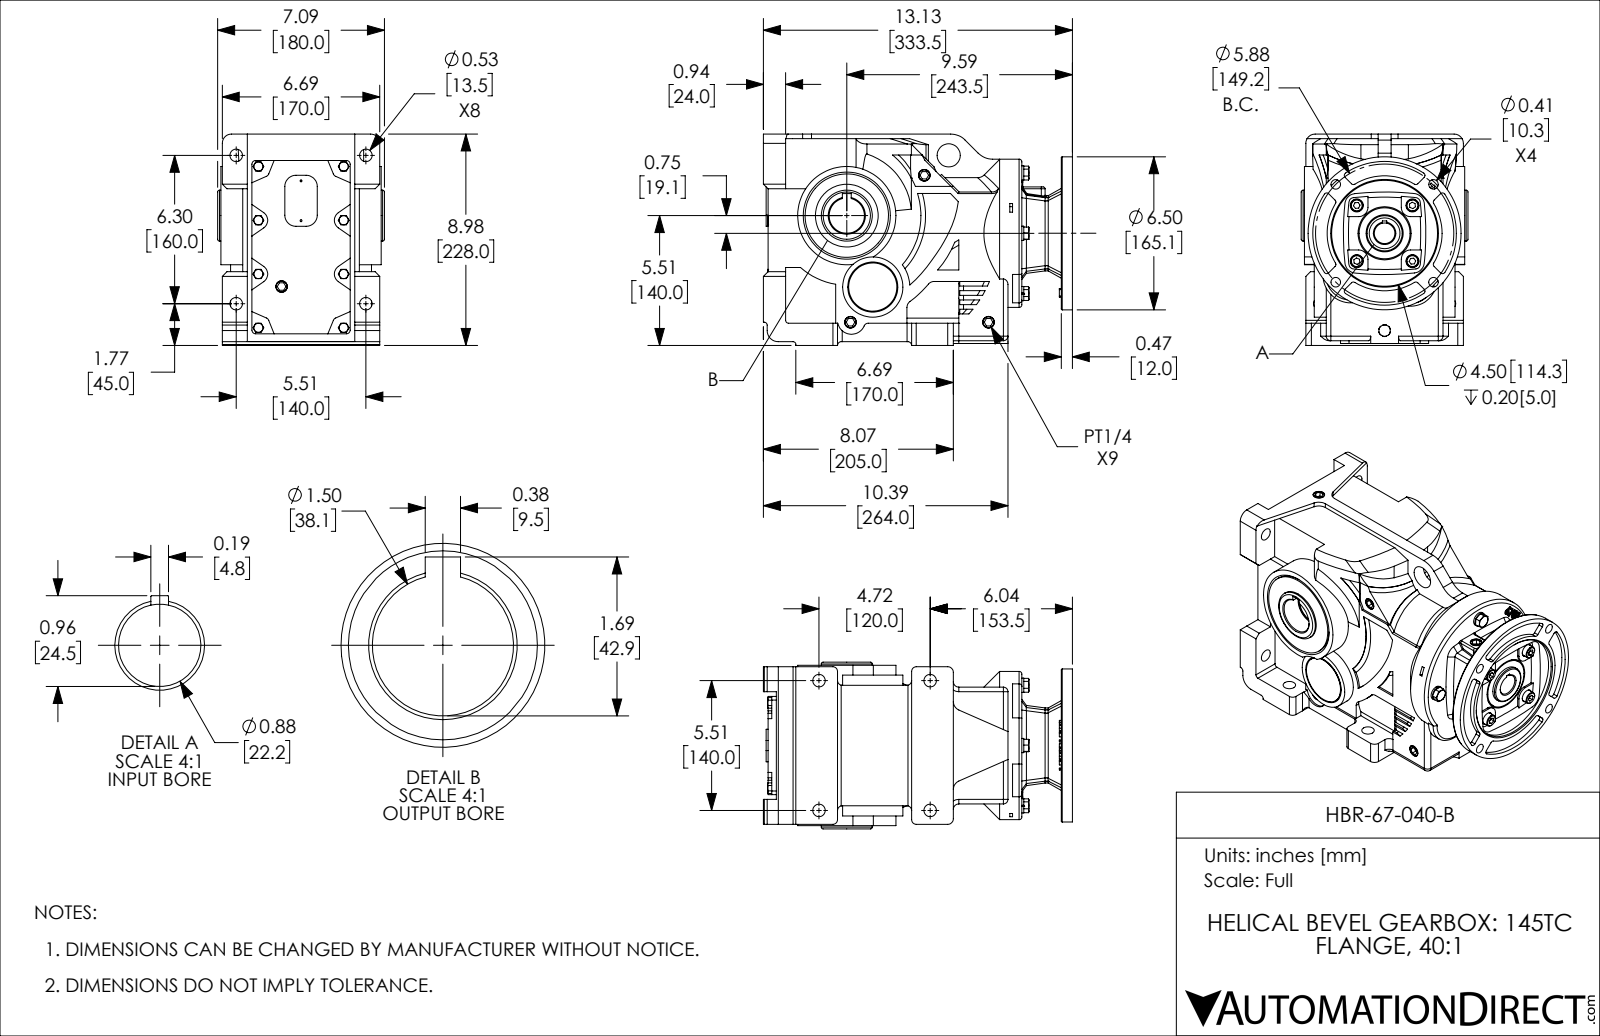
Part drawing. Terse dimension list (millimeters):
name: HBR-67-040-B
written by: SolidWorks 2018 (AUTOMOTIVE_DESIGN)
unit: mm
bodies: 1 solid, 1131 faces (598 planar, 268 cylindrical, 265 other)
size: 333.5 × 228 × 180
volume: 7 913 000 mm³; area: 412 300 mm²
holes: 8× ⌀13.5, 4× ⌀8.2, 4× ⌀9, 4× ⌀10.3, 4× ⌀14, 2× ⌀2, 1× ⌀22.2, 1× ⌀25, 1× ⌀28, 1× ⌀38.1, 1× ⌀40, 1× ⌀114.3
bosses: 4× ⌀15.4, 4× ⌀13, 4× ⌀8, 2× ⌀55, 1× ⌀165.1, 1× ⌀160, 1× ⌀106, 1× ⌀90
rounds: 20× R5, 19× R3, 15× R10, 12× R4, 7× R2, 5× R12, 4× R6, 4× R300
face distances: 5, 2, 24, 7, 1.5, 223, 126, 4, 3, 49.5
hole spacings: 54.2, 99.7, 32.1, 42.5, 46.1, 65, 74.6, 85.9
